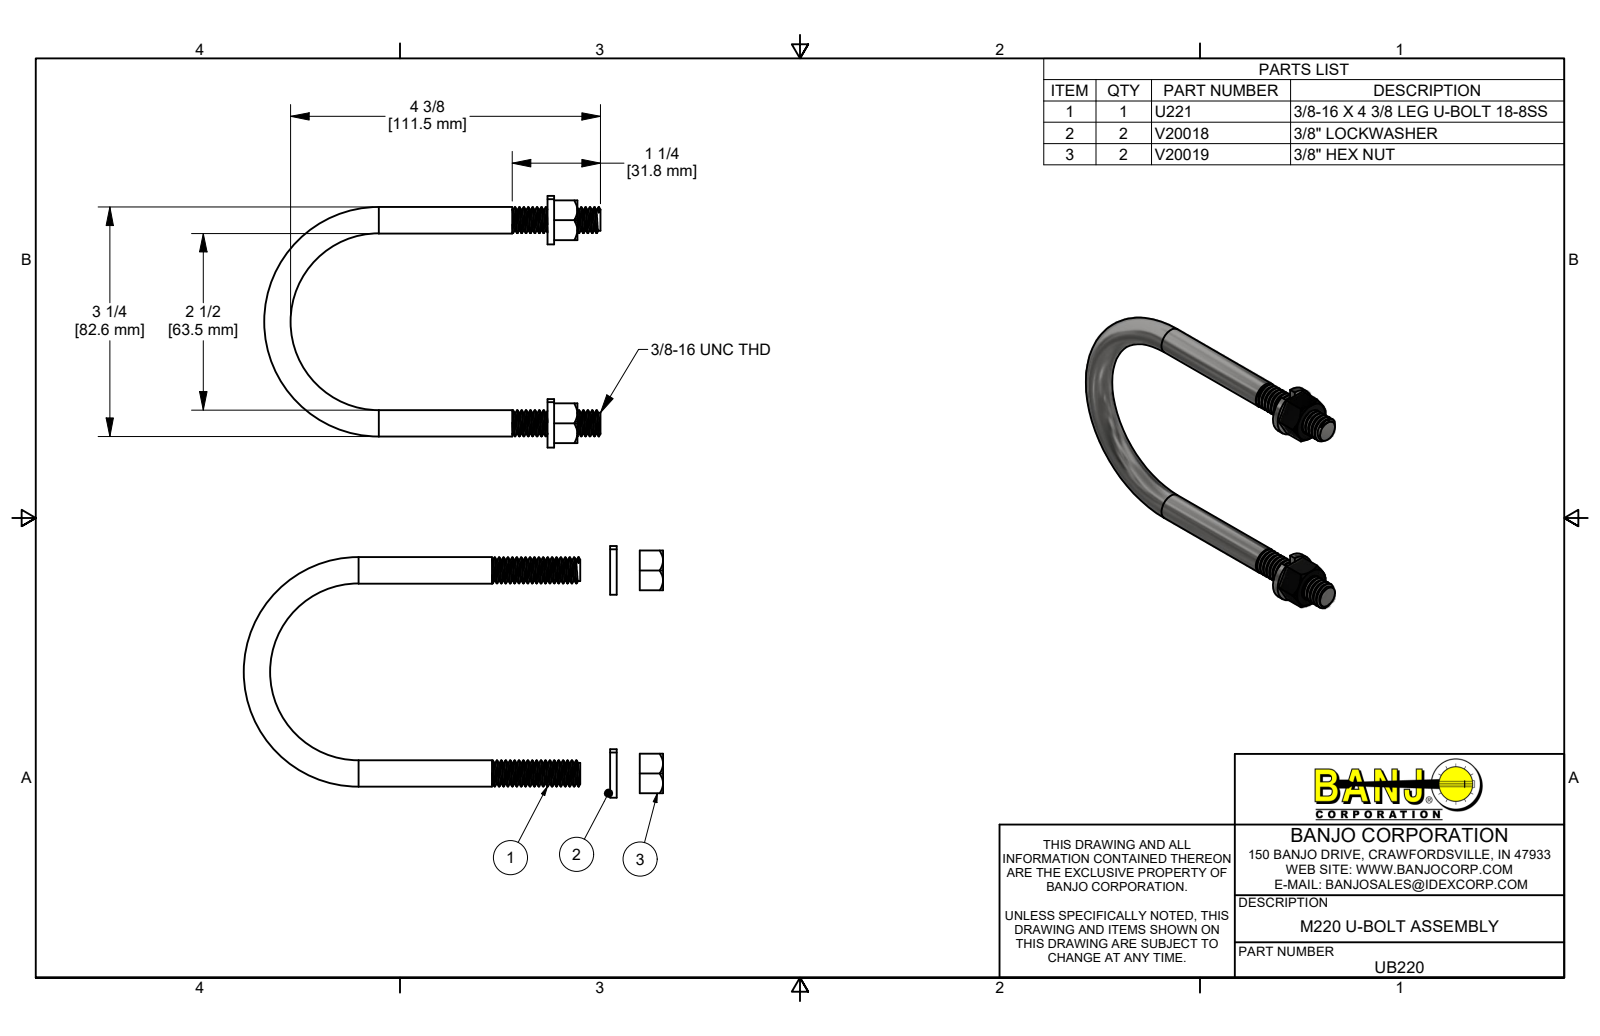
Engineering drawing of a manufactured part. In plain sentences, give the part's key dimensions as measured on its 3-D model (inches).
The part is named "UB220; U221; V20018; V20019". Its 3-D file was written by "Autodesk Inventor 2019 (AUTOMOTIVE_DESIGN)". It is 5 solids with 241 faces: 28 planar, 142 cylindrical and 71 other. Overall it measures 4.765 by 3.562 by 0.688 inches. Its volume is 1.315 cubic inches and its surface area 19.15 square inches. Round holes: 2 of diameter 0.307, 2 of diameter 0.375, 2 of diameter 0.385. Round bosses or shafts: 2 of diameter 0.687, 2 of diameter 0.367, 2 of diameter 0.3. Partial cylindrical surfaces (rounded edges, fillets, slot ends): 2 of radius 0.108. The main face-to-face distances are 0.563, 0.094, 1.437, 0.422, 0.328, 2, 0.875, 2.875, 0.75, 0.656. The hole center spacings are 2.875.
